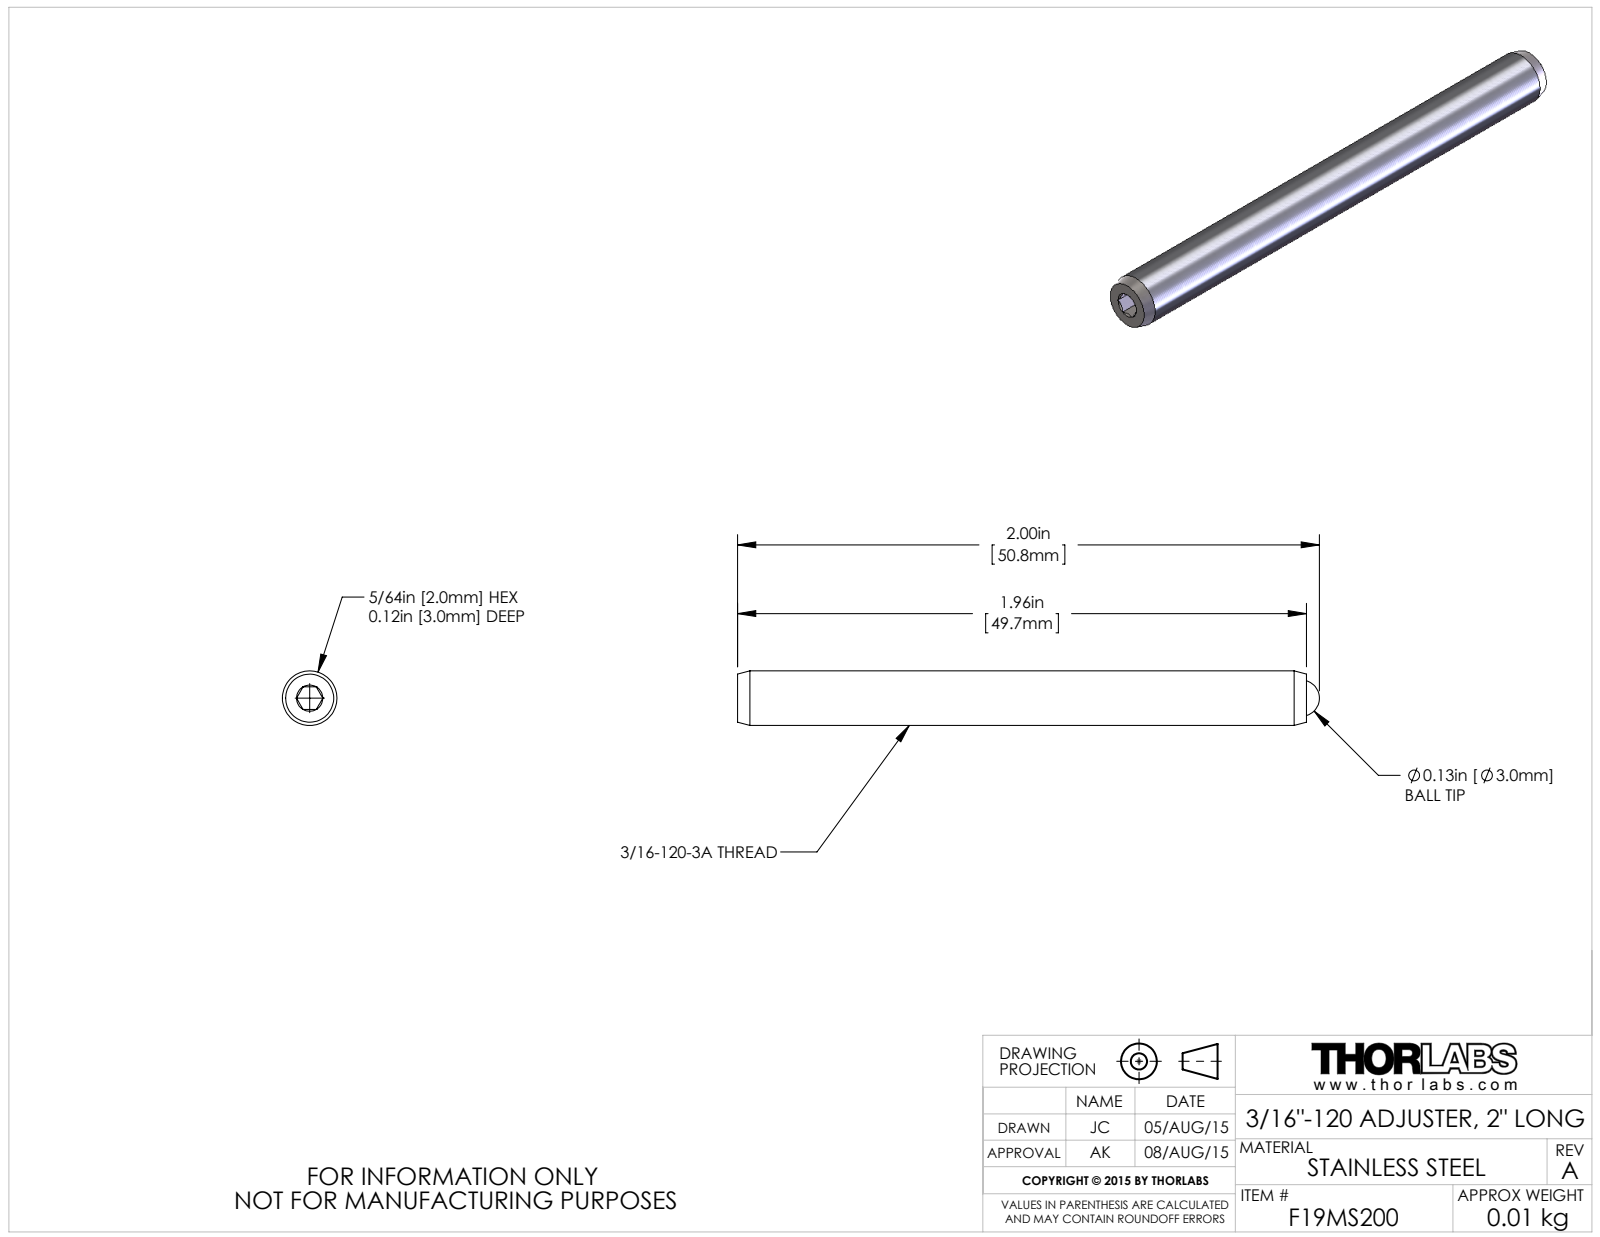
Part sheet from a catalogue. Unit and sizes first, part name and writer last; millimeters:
Units: millimetres
Overall size (bounding box): 50.8 × 4.8 × 4.8
Round holes (diameter × count): ⌀3.2 ×1
Round bosses / shafts (diameter × count): ⌀4.7 ×1
Main face-to-face distances: 2, 49.7, 3, 46.6
Volume: 870 mm³ · Surface area: 836 mm²
Bodies: 2 solids, 29 faces (9 planar, 4 cylindrical, 16 other)
Part name (STEP PRODUCT): TTN045708-E0W
STEP written by: SolidWorks 2014 (AUTOMOTIVE_DESIGN)
